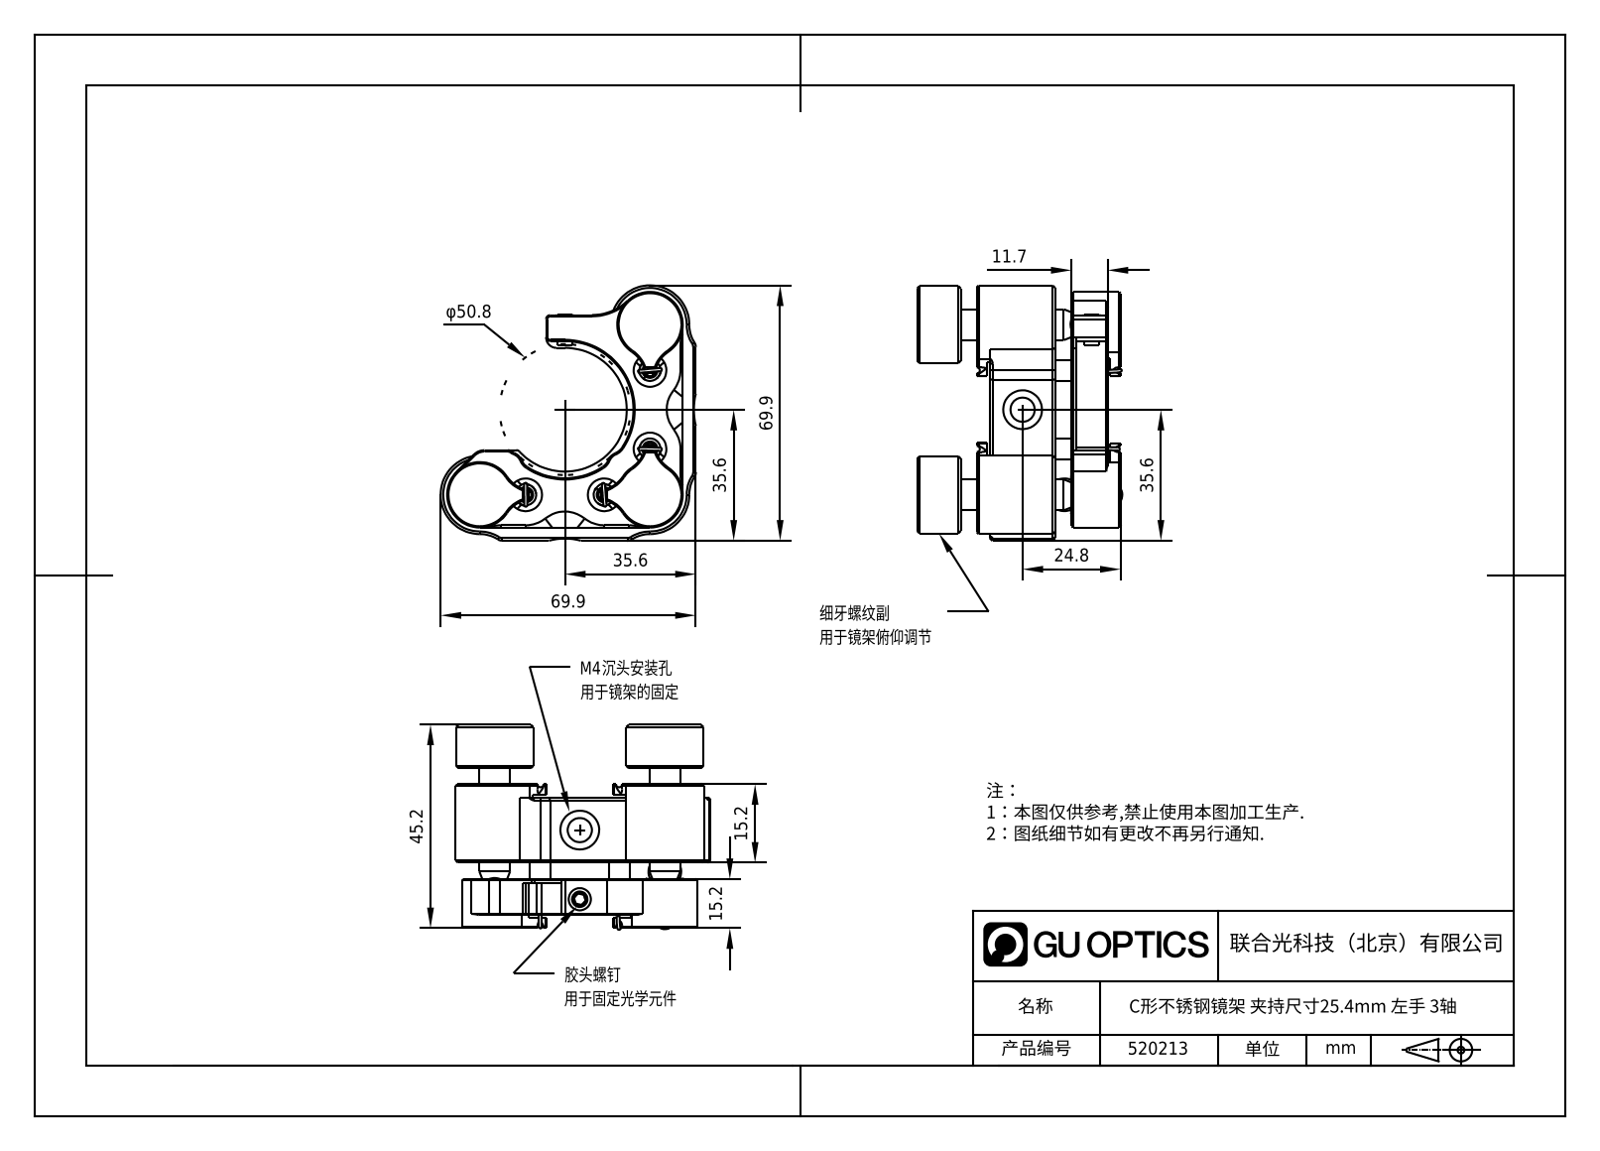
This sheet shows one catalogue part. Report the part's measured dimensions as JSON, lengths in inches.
{"part_name": "520213", "step_written_by": "SolidWorks 2020 (CONFIG_CONTROL_DESIGN)", "units": "inches", "bodies": {"solids": 23, "faces": 616, "planar": 221, "cylindrical": 140, "other": 255}, "overall_size": [2.75, 2.75, 1.785], "volume_in3": 2.391, "surface_area_in2": 37.32, "round_holes": [[0.25, 7], [0.185, 4], [0.297, 4], [0.071, 3], [0.157, 3], [0.157, 3], [0.236, 3], [0.276, 3], [0.079, 2], [0.13, 2]], "round_bosses_or_shafts": [[0.157, 8], [0.591, 3], [0.197, 3], [0.6, 2], [0.118, 2]], "partial_cylinders_radius": [[0.255, 19], [0.125, 8], [0.118, 5], [0.039, 4], [0.157, 4], [2.525, 4], [0.024, 3], [0.187, 3]], "face_to_face_distances": [0.5, 0.625, 0.1, 0.125, 0.6, 0.725, 1.225, 1.125, 1.056, 0.456], "hole_center_spacings": [0.372, 1.728, 0.374, 2.1, 2.133, 2.72, 0.197, 0.197]}
